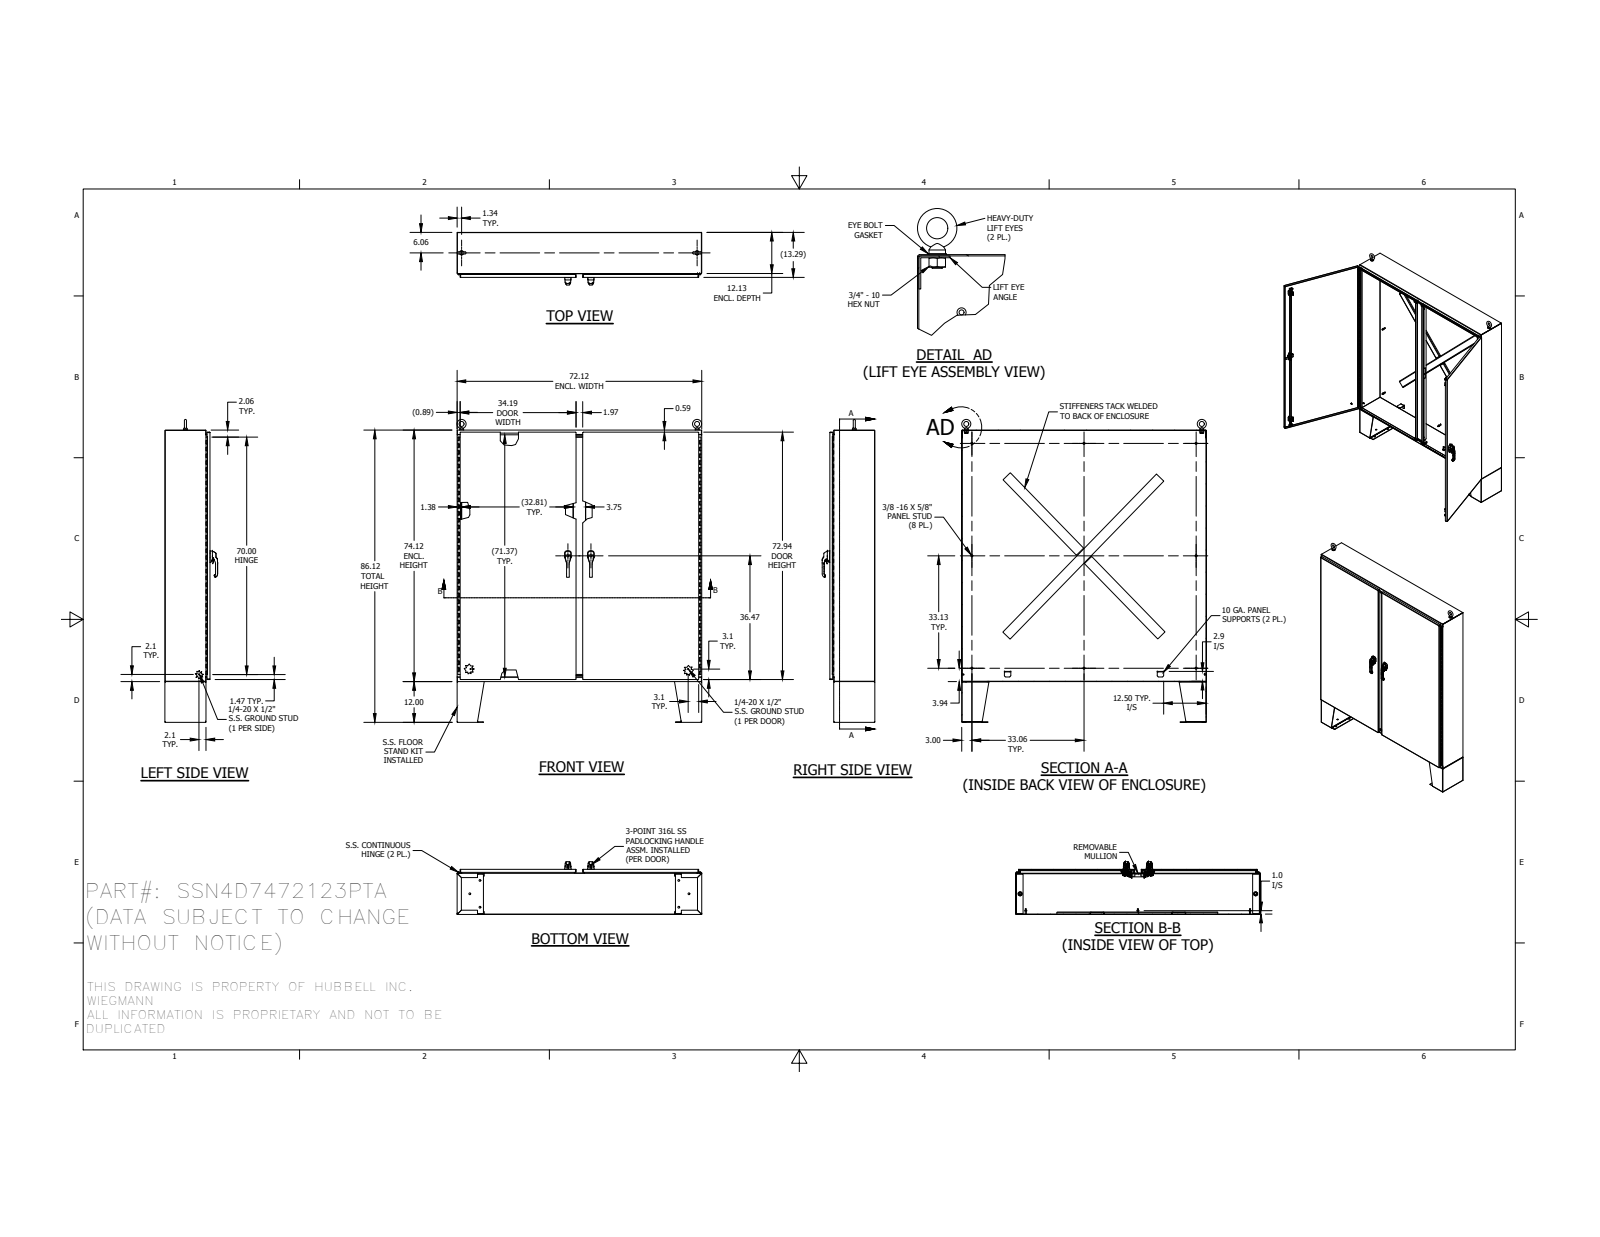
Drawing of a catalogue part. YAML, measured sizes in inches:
part_name: "1091-903_AF0_2_1; SSN4D72123PTBTM_1; 1225-05_1; HFW316325_1 (+8 more)"
step_written_by: "SolidWorks 2014 (AUTOMOTIVE_DESIGN)"
units: inches
bodies: {solids: 138, faces: 7352, planar: 2804, cylindrical: 2832, other: 1716}
overall_size: [89.248, 72.125, 15.538]
volume: 1716
surface_area: 36147
round_holes:
  - {diameter: 0.563, count: 18}
  - {diameter: 0.262, count: 16}
  - {diameter: 0.375, count: 16}
  - {diameter: 0.187, count: 8}
  - {diameter: 0.213, count: 6}
  - {diameter: 0.25, count: 6}
  - {diameter: 0.281, count: 6}
  - {diameter: 0.196, count: 4}
  - {diameter: 0.241, count: 4}
  - {diameter: 0.252, count: 4}
  - {diameter: 0.281, count: 4}
  - {diameter: 0.315, count: 4}
round_bosses_or_shafts:
  - {diameter: 0.33, count: 10}
  - {diameter: 0.625, count: 8}
  - {diameter: 0.25, count: 7}
  - {diameter: 1, count: 6}
  - {diameter: 0.533, count: 6}
  - {diameter: 0.236, count: 6}
  - {diameter: 0.563, count: 4}
  - {diameter: 0.531, count: 4}
partial_cylinders:
  - {radius: 0.02, count: 360}
  - {radius: 0.012, count: 213}
  - {radius: 0.019, count: 46}
  - {radius: 0.125, count: 46}
  - {radius: 0.05, count: 34}
  - {radius: 0.031, count: 32}
  - {radius: 0.079, count: 28}
  - {radius: 0.025, count: 24}
face_to_face_distances: [0.094, 13.193, 13.196, 13.1, 13.102, 13.287, 0.091, 13.29, 0.096, 72.031]
hole_center_spacings: [15.556, 0.38, 0.38, 0.76, 7.778, 31.111, 64.052, 64.427]
